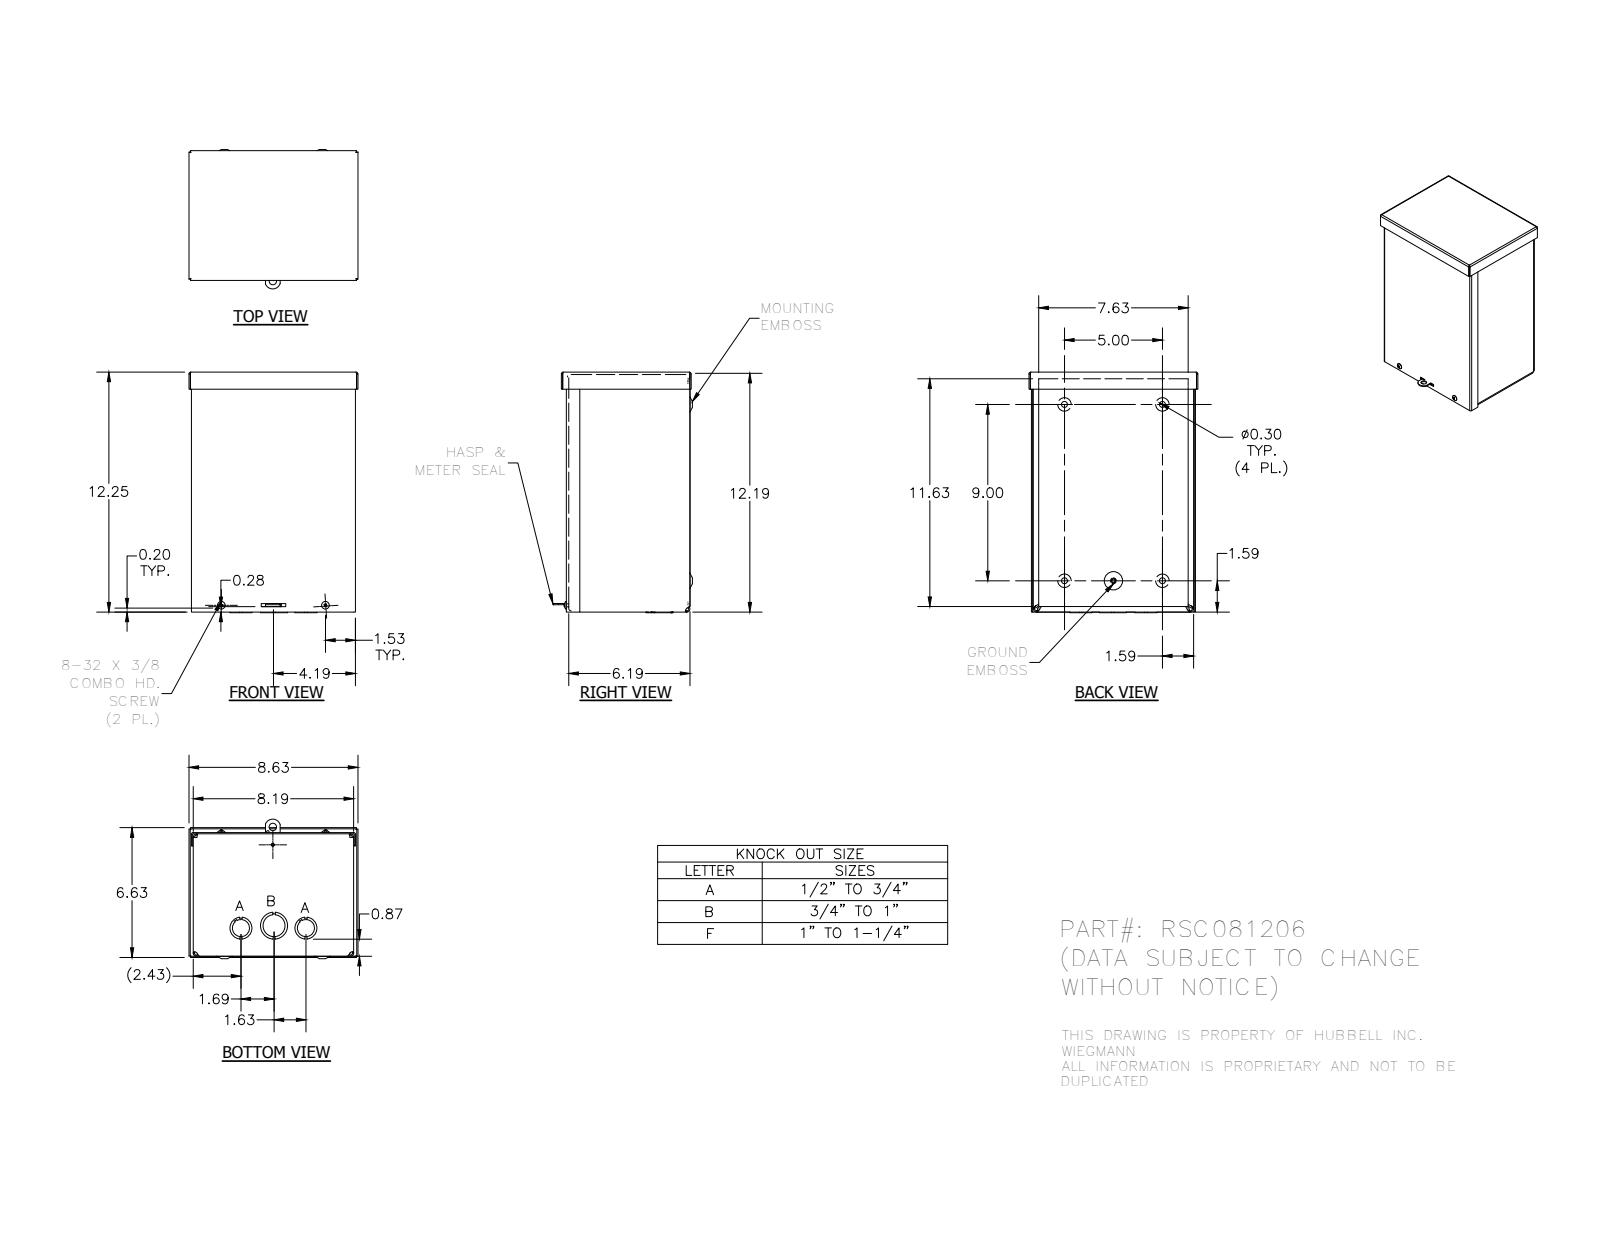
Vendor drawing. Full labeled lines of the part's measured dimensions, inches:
Part name (STEP PRODUCT): RSC081206; RSC081206_WRAP; RSC0812_LID; RSC0806_CAP (+4 more)
STEP written by: Autodesk Inventor 2012 (AUTOMOTIVE_DESIGN)
Units: inches
Bodies: 7 solids, 503 faces (238 planar, 121 cylindrical, 144 other)
Overall size (bounding box): 12.281 × 8.625 × 7.125
Volume: 36.63 in³ · Surface area: 1 197 in²
Round holes (diameter × count): ⌀0.3 ×4, ⌀0.313 ×4, ⌀1.125 ×3, ⌀0.125 ×2, ⌀0.148 ×2, ⌀0.875 ×2, ⌀0.156 ×1, ⌀0.165 ×1, ⌀0.375 ×1, ⌀1.375 ×1
Round bosses / shafts (diameter × count): ⌀0.384 ×2, ⌀0.164 ×2, ⌀0.229 ×1
Partial cylindrical surfaces — rounded edges, fillets, slot ends (radius × count): R0.01 ×10, R0.031 ×8, R0.093 ×8, R0.125 ×8, R0.187 ×8, R0.021 ×4, R0.031 ×4, R0.055 ×4
Main face-to-face distances: 0.062, 8.126, 0.062, 6.249, 6.187, 0.063, 12.126, 6.312, 6.25, 0.124
Hole centre spacings: 1.072, 1.261, 2.5, 5, 5.313, 9, 9.341, 10.062
